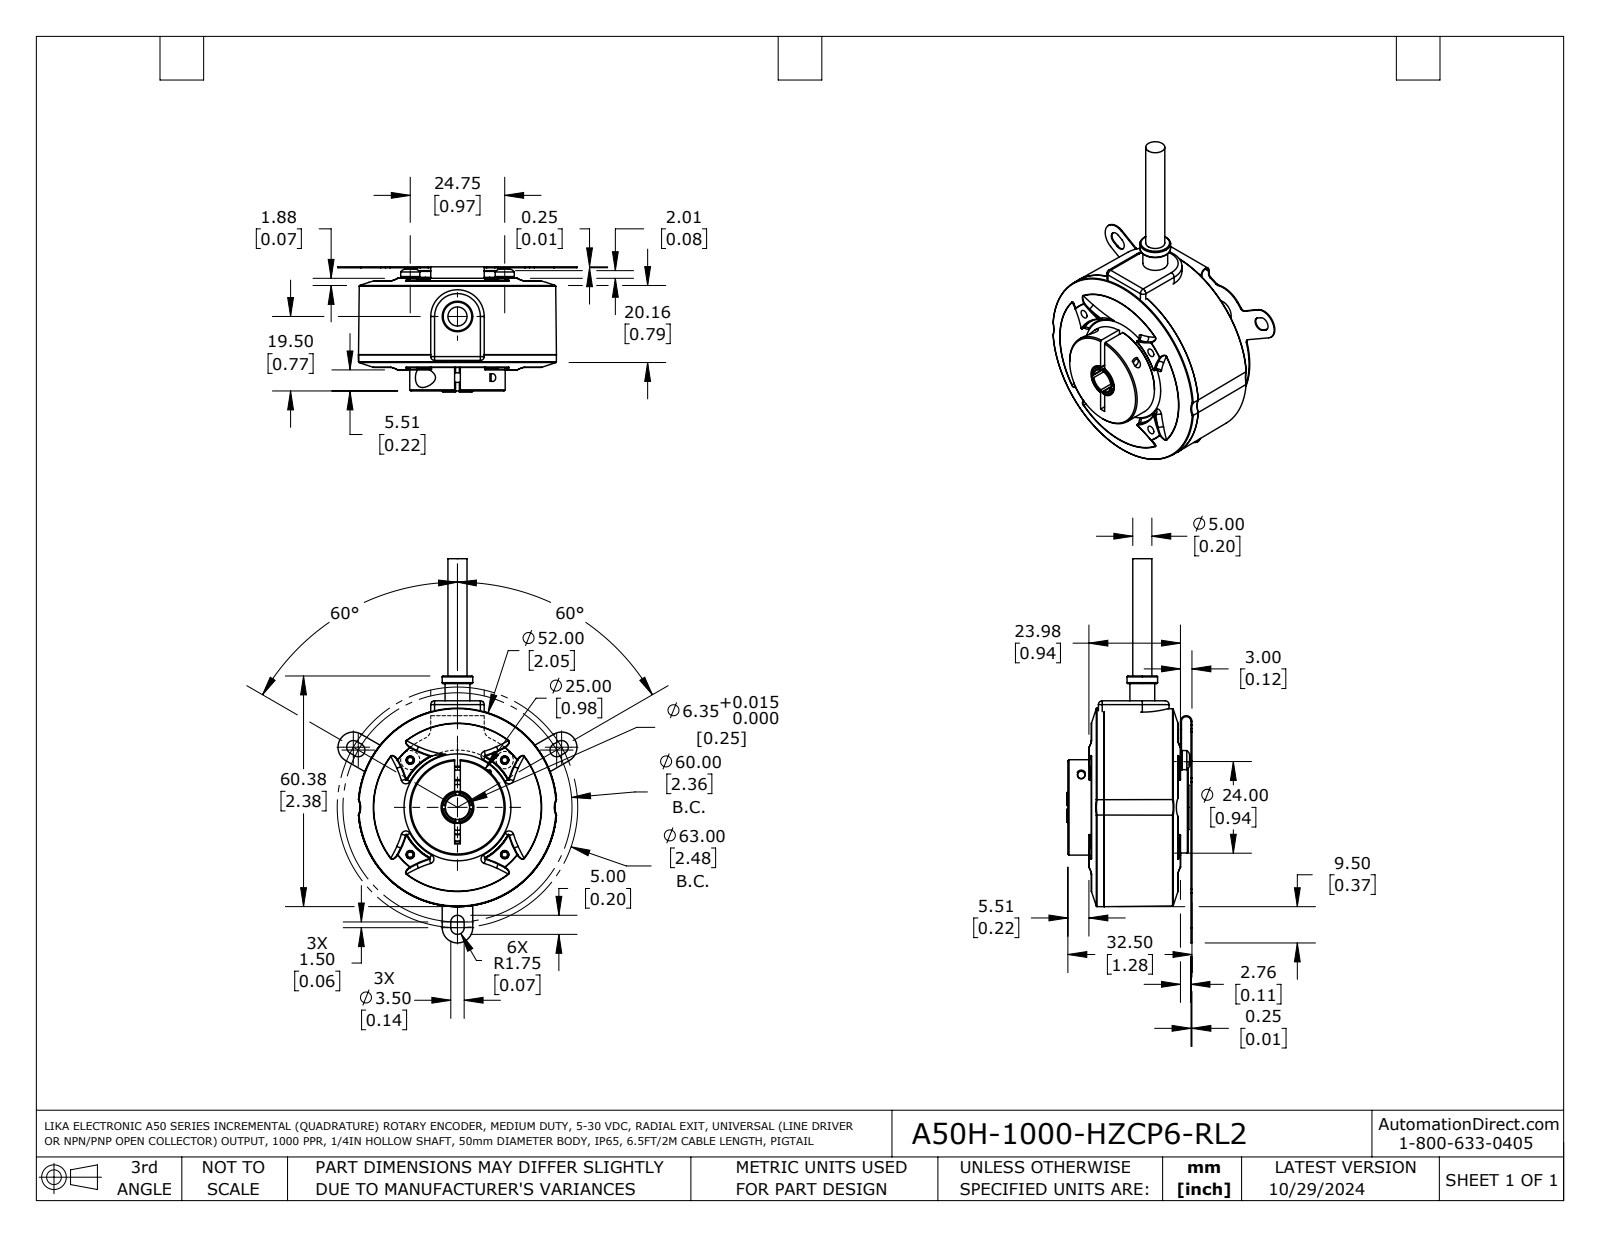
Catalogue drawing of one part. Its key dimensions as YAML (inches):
part_name: "A50H-1000-HZCP6-RL2"
step_written_by: "SolidWorks 2021 (AUTOMOTIVE_DESIGN)"
units: inches
bodies: {solids: 14, faces: 954, planar: 160, cylindrical: 259, other: 535}
overall_size: [3.961, 2.464, 1.291]
volume: 1.39
surface_area: 43.48
round_holes:
  - {diameter: 0.11, count: 5}
  - {diameter: 0.217, count: 2}
  - {diameter: 0.236, count: 2}
  - {diameter: 0.081, count: 1}
  - {diameter: 0.205, count: 1}
  - {diameter: 0.25, count: 1}
  - {diameter: 0.315, count: 1}
  - {diameter: 0.579, count: 1}
  - {diameter: 0.728, count: 1}
  - {diameter: 1.024, count: 1}
round_bosses_or_shafts:
  - {diameter: 0.098, count: 5}
  - {diameter: 0.197, count: 4}
  - {diameter: 0.984, count: 1}
  - {diameter: 0.827, count: 1}
  - {diameter: 0.709, count: 1}
  - {diameter: 0.571, count: 1}
  - {diameter: 0.472, count: 1}
  - {diameter: 0.315, count: 1}
partial_cylinders:
  - {radius: 0.007, count: 24}
  - {radius: 0.015, count: 24}
  - {radius: 0.039, count: 18}
  - {radius: 0.004, count: 6}
  - {radius: 0.069, count: 6}
  - {radius: 0.984, count: 5}
  - {radius: 0.157, count: 3}
  - {radius: 0.02, count: 2}
face_to_face_distances: [0.118, 0.079, 0.787, 0.197, 0.669, 0.866, 0.896, 0.276, 0.748, 0.098]
hole_center_spacings: [0.583, 0.689, 0.807, 1.383, 0.974, 1.614]
